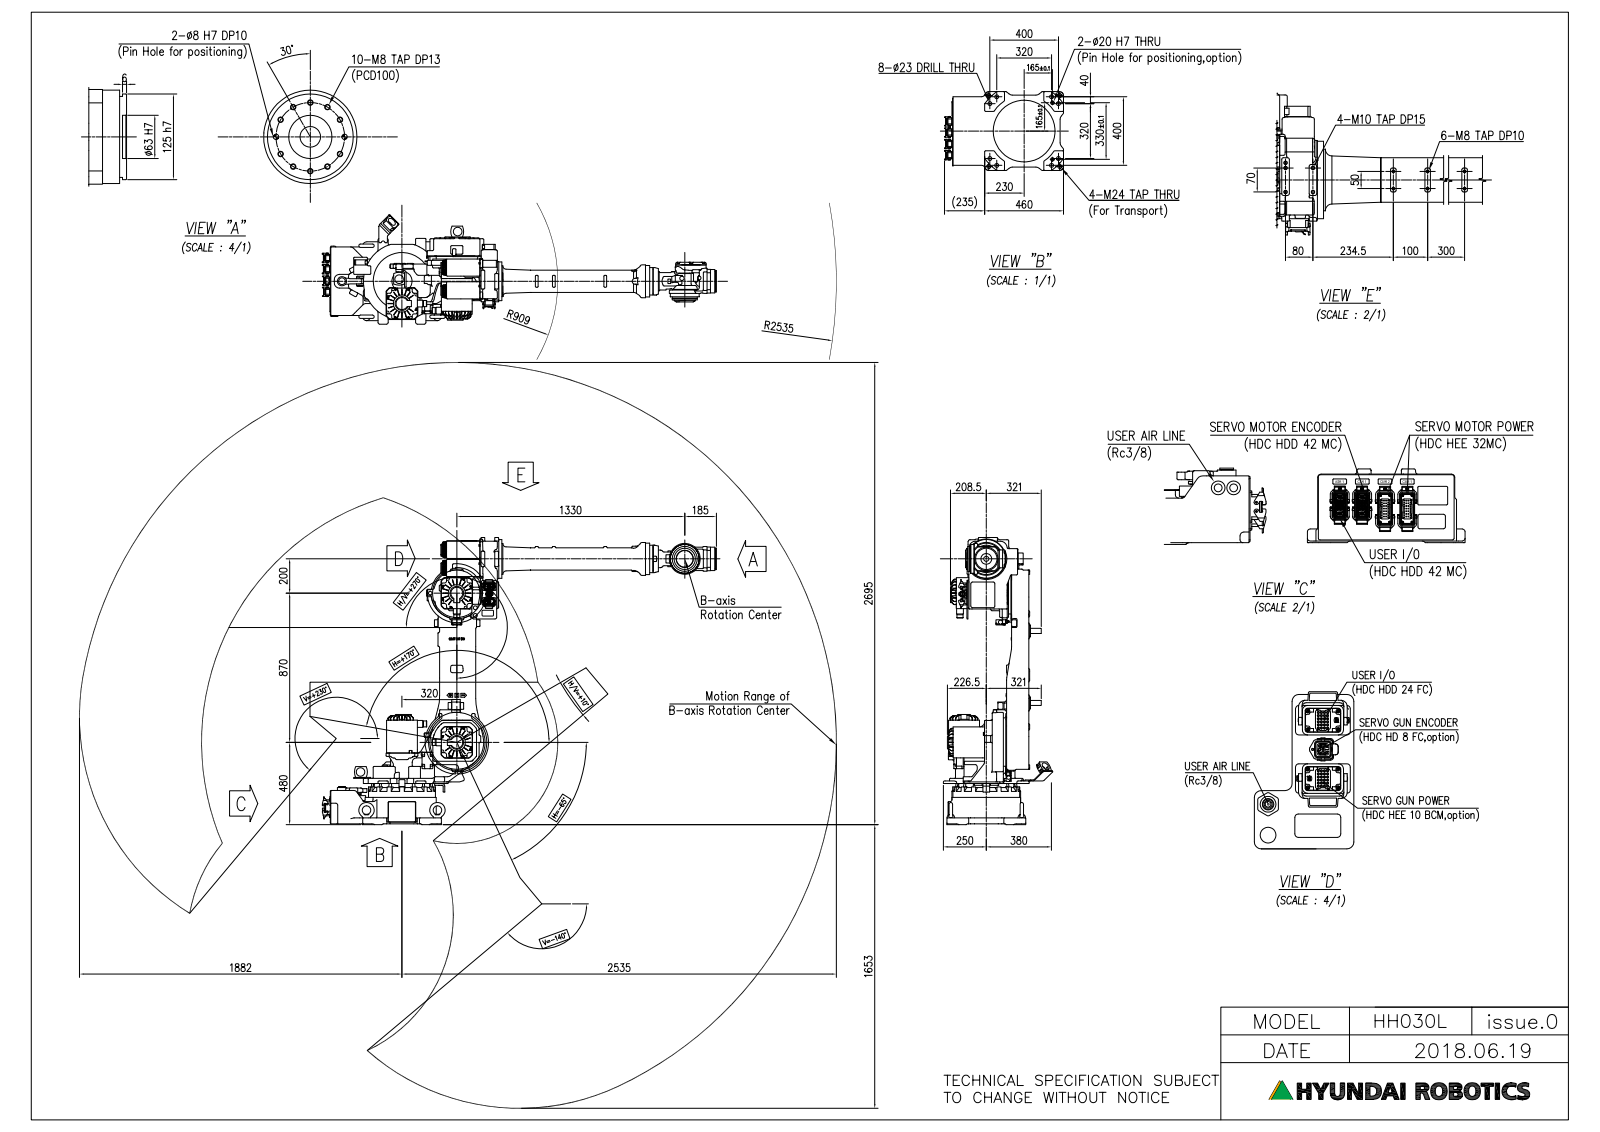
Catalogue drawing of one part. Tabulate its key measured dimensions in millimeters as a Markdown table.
| quantity | value |
| --- | --- |
| part name | HH030L_ARM FRAME; HH030L_BASE BODY; HH030L; HH030L_B REDUCER (+8 more) |
| STEP written by | SolidWorks 2017 (AUTOMOTIVE_DESIGN) |
| units | millimeters |
| bodies | 29 solids, 2398 faces (1603 planar, 741 cylindrical, 54 other) |
| overall size | 2250 × 1680 × 500 |
| volume | 161 600 000 mm³ |
| surface area | 7 360 000 mm² |
| round holes (diameter × count) | 6 × 6, 114.3 × 2, 245 × 2, 250 × 2, 30 × 1, 39 × 1, 58 × 1, 63 × 1, 70 × 1, 95 × 1, 100 × 1, 105 × 1 |
| round bosses / shafts (diameter × count) | 80 × 3, 60 × 3, 35 × 3, 180 × 2, 125 × 2, 120 × 2, 100 × 2, 30 × 2 |
| partial cylindrical surfaces (radius × count) | 5 × 43, 25 × 22, 10 × 15, 30 × 15, 6 × 12, 6.5 × 12, 35 × 9, 17.5 × 8 |
| main face-to-face distances | 230, 30, 48, 35, 18, 70, 50, 138, 212, 102 |
| hole center spacings | 53.03, 57.01, 72.89, 75, 75.37, 109.83, 111.5, 116.22 |
